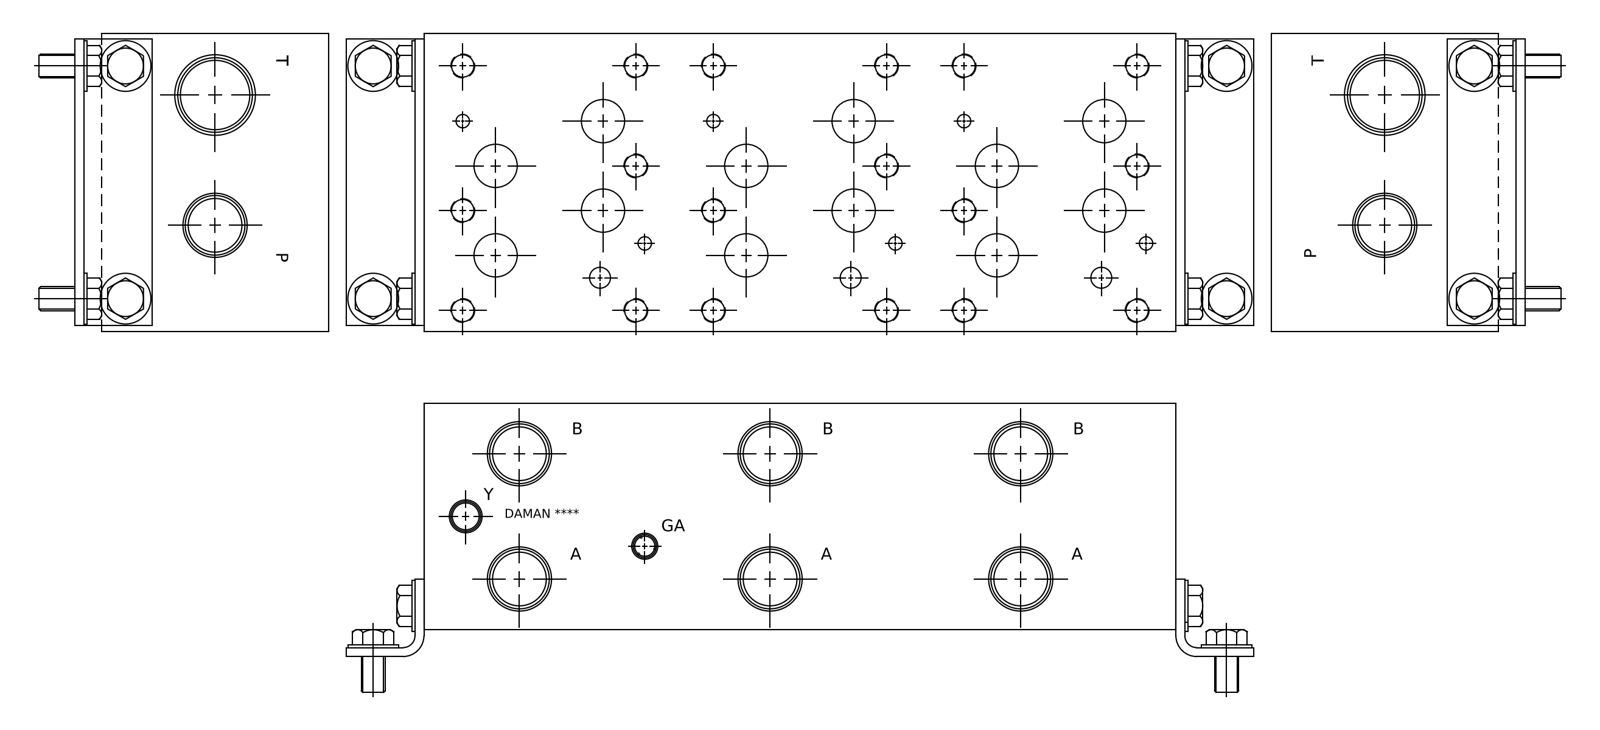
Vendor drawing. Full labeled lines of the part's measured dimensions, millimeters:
Part name (STEP PRODUCT): Part_AD08P035P_3D
STEP written by: Autodesk Inventor 2019 (AUTOMOTIVE_DESIGN)
Units: millimetres
Bodies: 1 solid, 726 faces (395 planar, 93 cylindrical, 238 other)
Overall size (bounding box): 400.05 × 158.75 × 120.65
Volume: 7 230 000 mm³ · Surface area: 332 917 mm²
Round holes (diameter × count): ⌀10.72 ×21, ⌀12.7 ×20, ⌀23.01 ×11, ⌀28.57 ×7, ⌀33.71 ×7, ⌀7.14 ×6, ⌀11.13 ×2, ⌀11.11 ×1, ⌀13.87 ×1, ⌀14.3 ×1, ⌀17.3 ×1, ⌀23.02 ×1
Main face-to-face distances: 120.65, 158.75, 400.05, 19, 139.75, 19.51, 380.54, 90.42, 30.23, 381.05
Hole centre spacings: 133.35, 266.7, 61.92, 74.63, 118.29, 152.7, 191.98, 29.53
